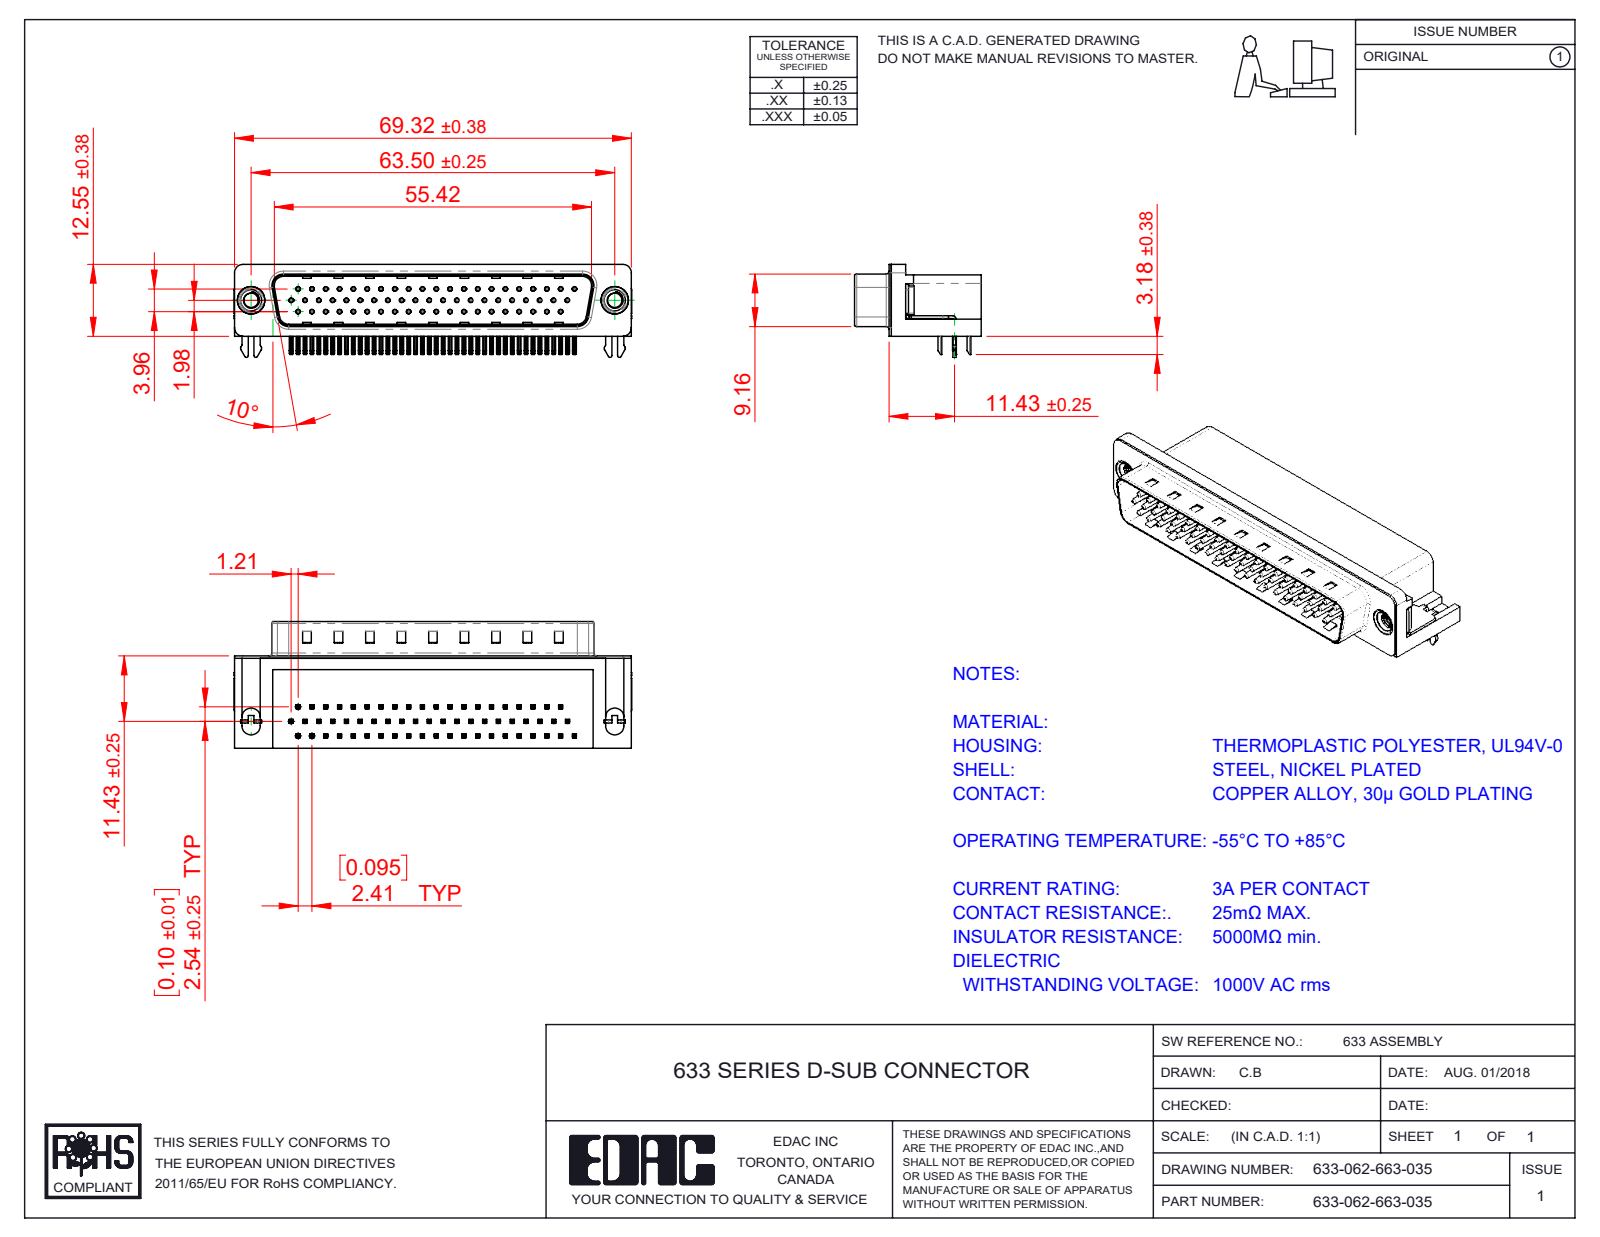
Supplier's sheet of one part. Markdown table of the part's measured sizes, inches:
| quantity | value |
| --- | --- |
| part name | 633-062-663-035; 633 Contact Bottom; 633 2 Prong Board Lock; 633 Housing_62 Contact (+4 more) |
| STEP written by | SolidWorks 2016 (CONFIG_CONTROL_DESIGN) |
| units | inches |
| bodies | 68 solids, 5116 faces (3245 planar, 1454 cylindrical, 417 other) |
| overall size | 2.732 × 0.87 × 0.64 |
| volume | 0.674 in³ |
| surface area | 20.79 in² |
| round holes (diameter × count) | 0.014 × 62, 0.031 × 62, 0.098 × 2, 0.157 × 2, 0.189 × 2, 0.197 × 2 |
| round bosses / shafts (diameter × count) | 0.03 × 62, 0.193 × 2, 0.187 × 2, 0.154 × 2 |
| partial cylindrical surfaces (radius × count) | 0.01 × 256, 0.005 × 124, 0.039 × 16, 0.02 × 14, 0.063 × 8, 0.059 × 7, 0.013 × 4, 0.035 × 4 |
| main face-to-face distances | 0.016, 0.407, 0.618, 0.345, 0.114, 0.098, 0.1, 0.083, 0.329, 0.634 |
| hole center spacings | 0.095, 0.19, 0.285, 0.38, 0.57, 0.665, 0.19, 0.285 |
